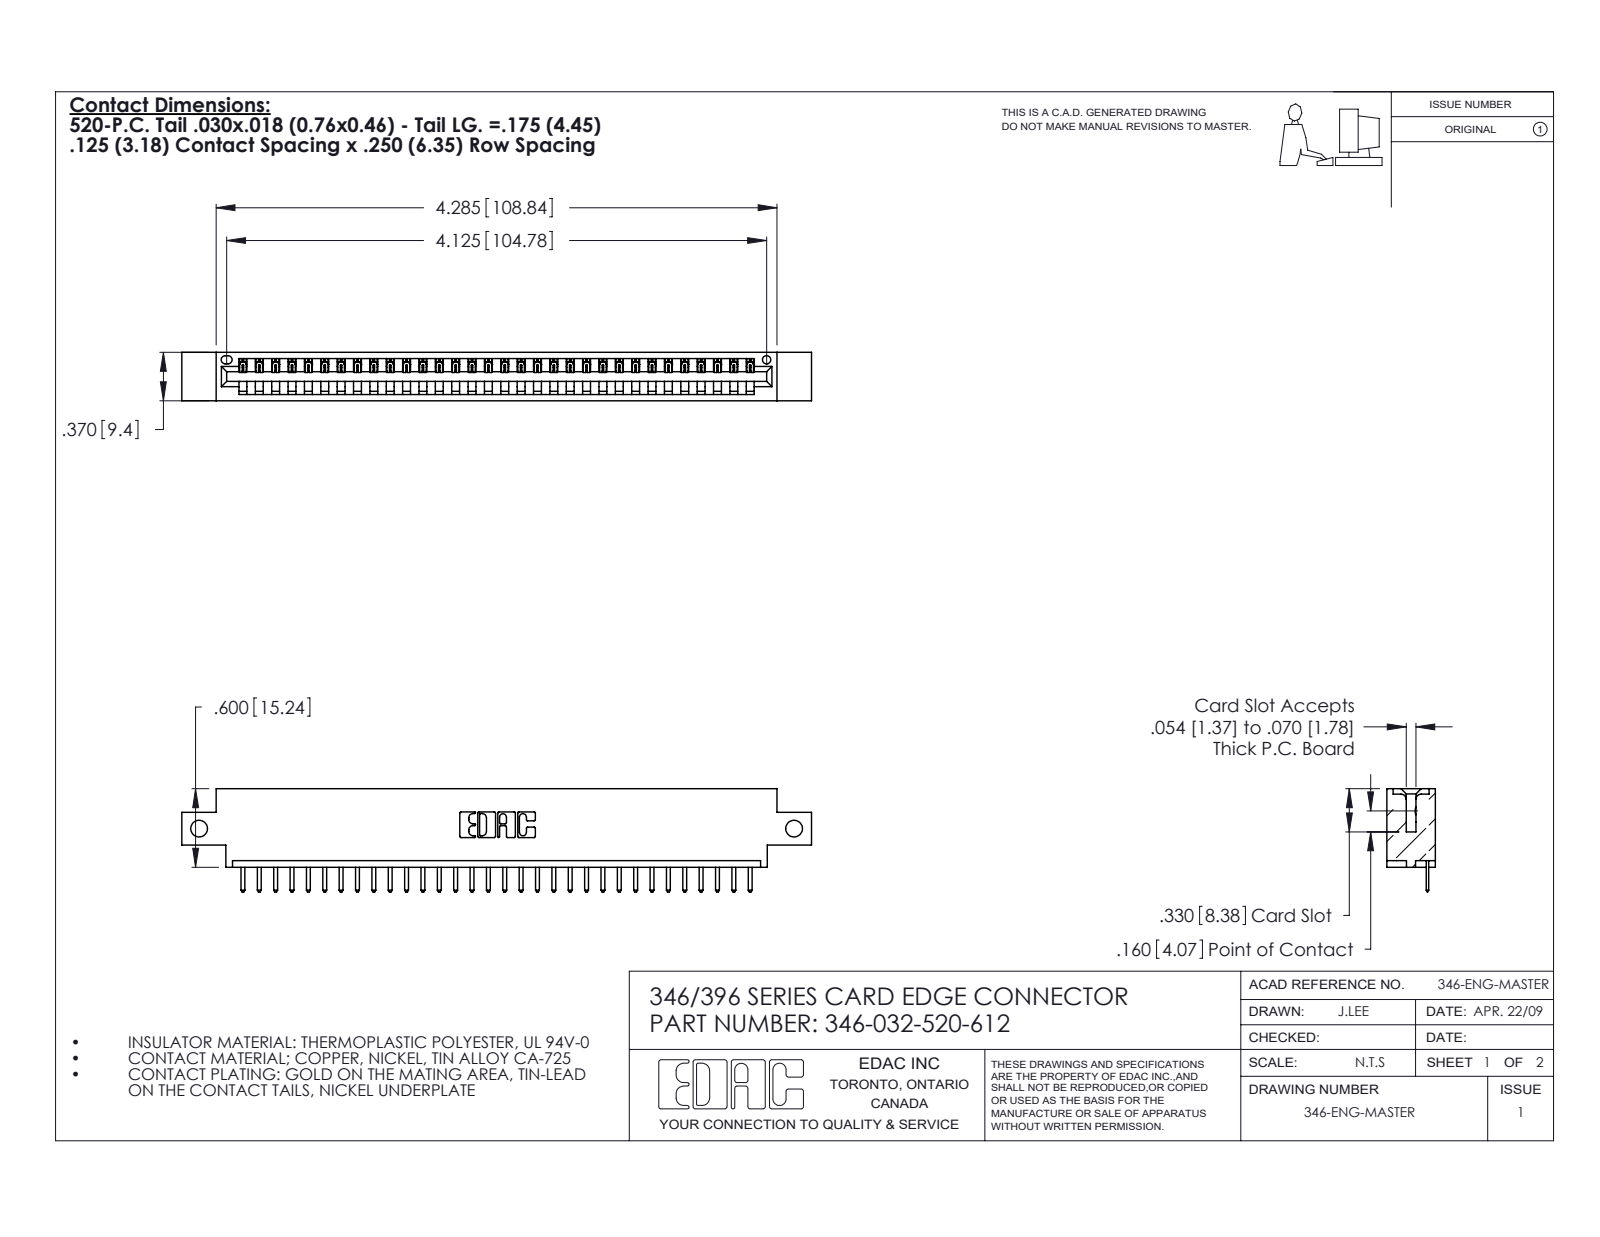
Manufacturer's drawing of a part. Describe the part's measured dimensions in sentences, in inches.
The part is named "346 Part_0.170 Offset - Side Mount; 345-292-001_345-293-120; 346-032-520-612". Its 3-D file was written by "SolidWorks 2020 (CONFIG_CONTROL_DESIGN)". It is 33 solids with 2110 faces: 1424 planar, 686 cylindrical and 0 other. Overall it measures 4.81 by 0.788 by 0.37 inches. Its volume is 0.689 cubic inches and its surface area 21.25 square inches. Round holes: 2 of diameter 0.128, 1 of diameter 0.064. Partial cylindrical surfaces (rounded edges, fillets, slot ends): 66 of radius 0.01, 64 of radius 0.006, 22 of radius 0.01, 6 of radius 0.007, 6 of radius 0.031, 3 of radius 0.026, 2 of radius 0.031, 2 of radius 0.04. The main face-to-face distances are 0.048, 0.322, 0.37, 0.25, 0.148, 0.222, 0.1, 0.174, 0.072, 0.298. The hole center spacings are 4.545.
